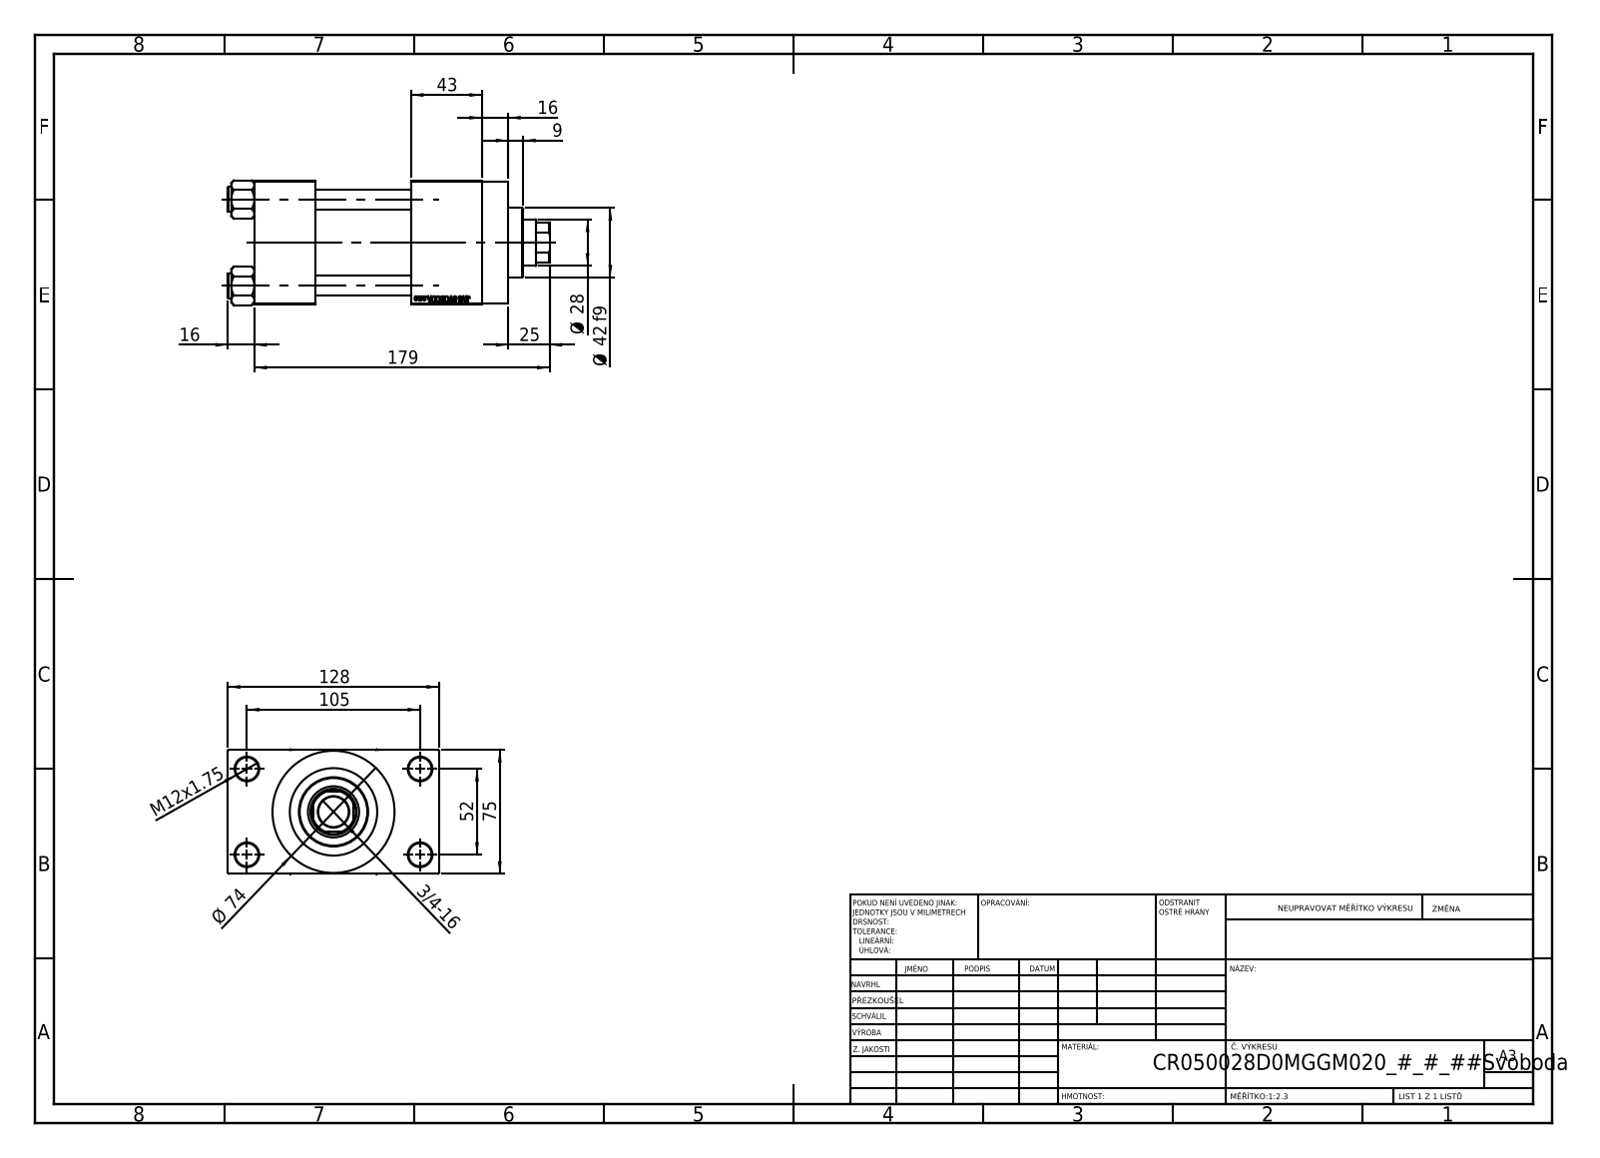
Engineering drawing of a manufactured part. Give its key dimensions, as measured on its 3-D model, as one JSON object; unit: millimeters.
{"part_name": "V215_VC_A; NUT_M5_D; V215CR_D_TYCINKA; V215CR_D_Body (+1 more)", "step_written_by": "SolidWorks 2019 (CONFIG_CONTROL_DESIGN)", "units": "millimeters", "bodies": {"solids": 11, "faces": 1104, "planar": 497, "cylindrical": 89, "other": 518}, "overall_size": [195, 128, 75.54], "volume_mm3": 815231, "surface_area_mm2": 168868, "round_holes": [[12, 4], [14, 4], [7, 2], [20.96, 2], [30, 2], [18.5, 1], [28, 1], [31, 1], [41, 1], [50, 1], [53, 1]], "round_bosses_or_shafts": [[15, 4], [74, 1], [56, 1], [42, 1]], "partial_cylinders_radius": [[13.5, 1]], "face_to_face_distances": [75, 58, 37, 95, 26.5, 101.5, 138, 101, 43, 16], "hole_center_spacings": [26.35, 36.98, 52.3, 58.43, 58.59, 78.65, 94.37, 52]}
